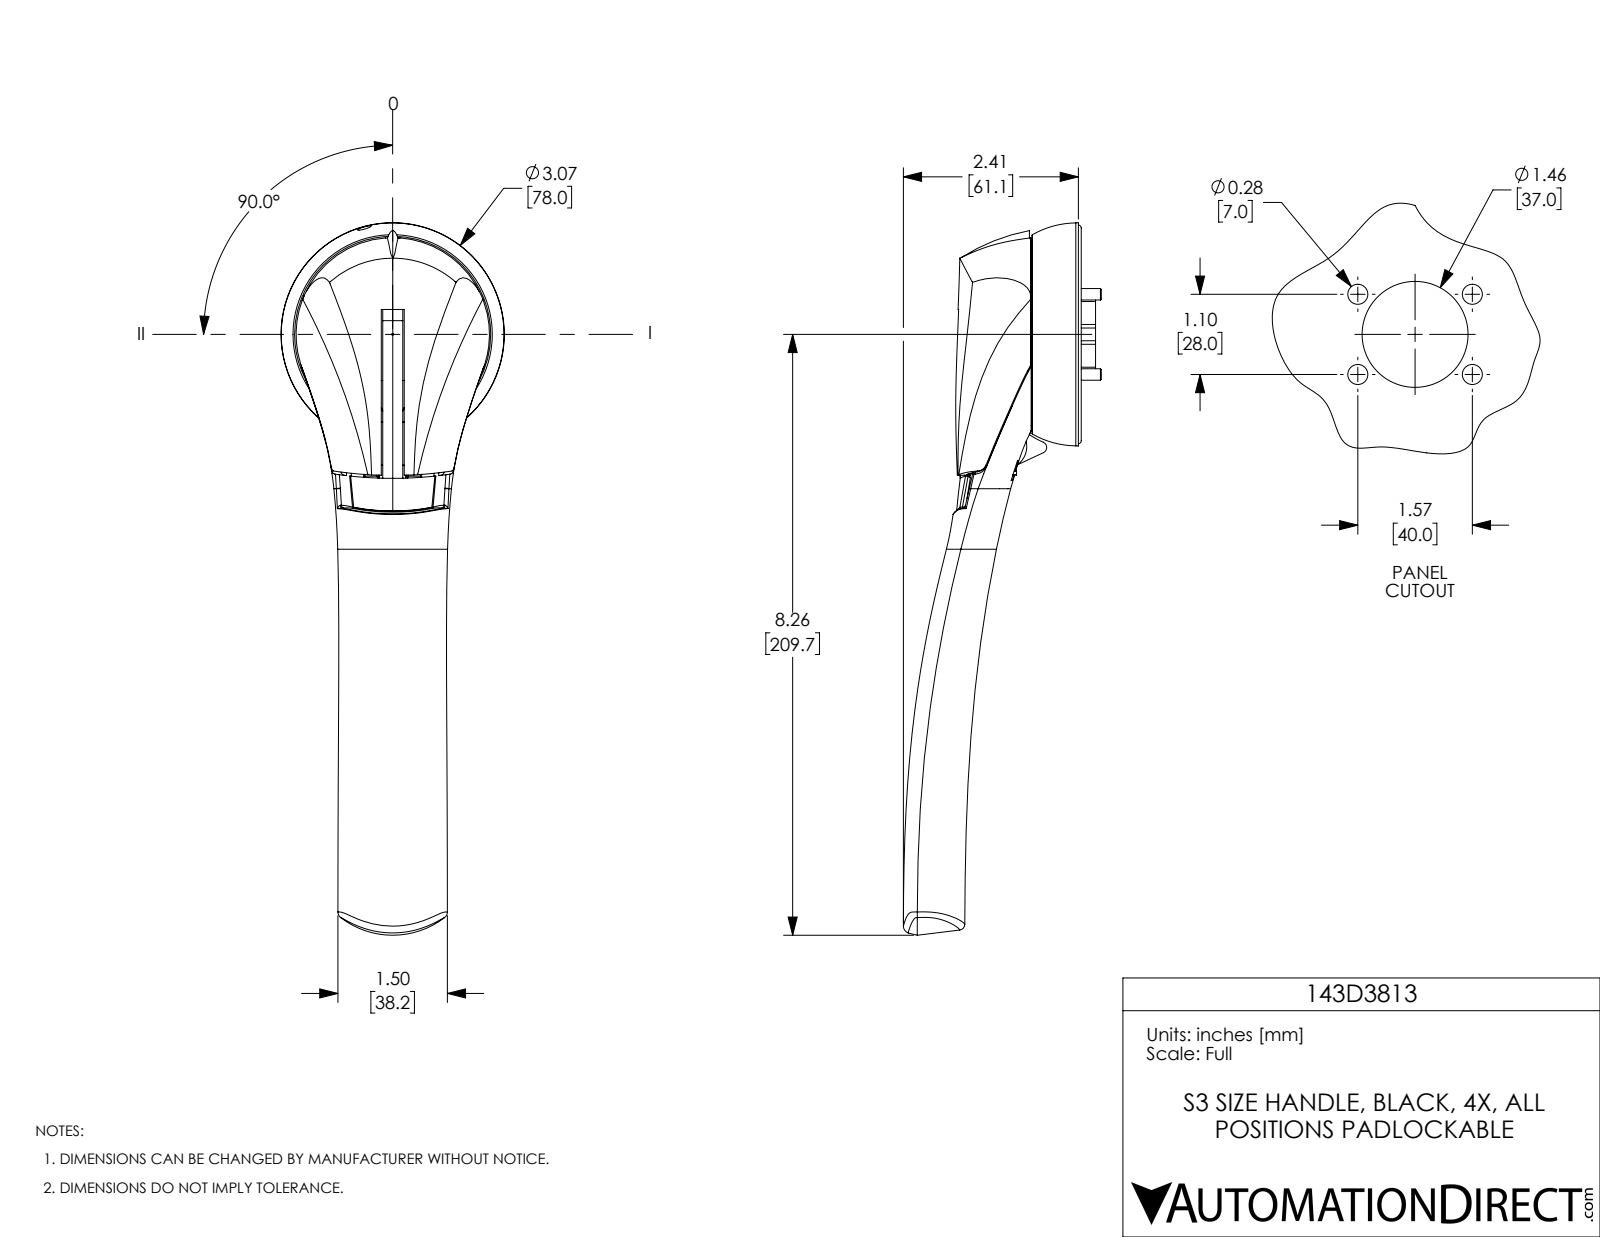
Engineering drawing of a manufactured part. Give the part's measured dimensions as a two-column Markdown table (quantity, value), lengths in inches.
| quantity | value |
| --- | --- |
| part name | 143D3813 |
| STEP written by | SolidWorks 2017 (AUTOMOTIVE_DESIGN) |
| units | inches |
| bodies | 8 solids, 1514 faces (806 planar, 544 cylindrical, 164 other) |
| overall size | 9.793 × 3.07 × 2.721 |
| volume | 12.91 in³ |
| surface area | 100.4 in² |
| round holes (diameter × count) | 0.157 × 6, 0.339 × 4, 0.425 × 4, 0.03 × 3, 0.169 × 2, 0.362 × 2, 0.118 × 1, 0.189 × 1, 2.992 × 1 |
| round bosses / shafts (diameter × count) | 0.02 × 11, 0.335 × 4, 0.315 × 4, 0.089 × 3, 0.069 × 3, 0.228 × 2, 2.819 × 1, 2.701 × 1 |
| partial cylindrical surfaces (radius × count) | 0.01 × 221, 0.015 × 20, 0.034 × 20, 0.03 × 15, 0.039 × 4, 0.025 × 3, 5.437 × 3, 0.079 × 2 |
| main face-to-face distances | 0.024, 0.701, 0.713, 0.689, 0.035, 0.276, 0.102, 0.173, 0.244, 0.047 |
| hole center spacings | 0.961, 0.309, 0.669, 1.098, 1.102, 1.203, 1.575, 1.881 |
